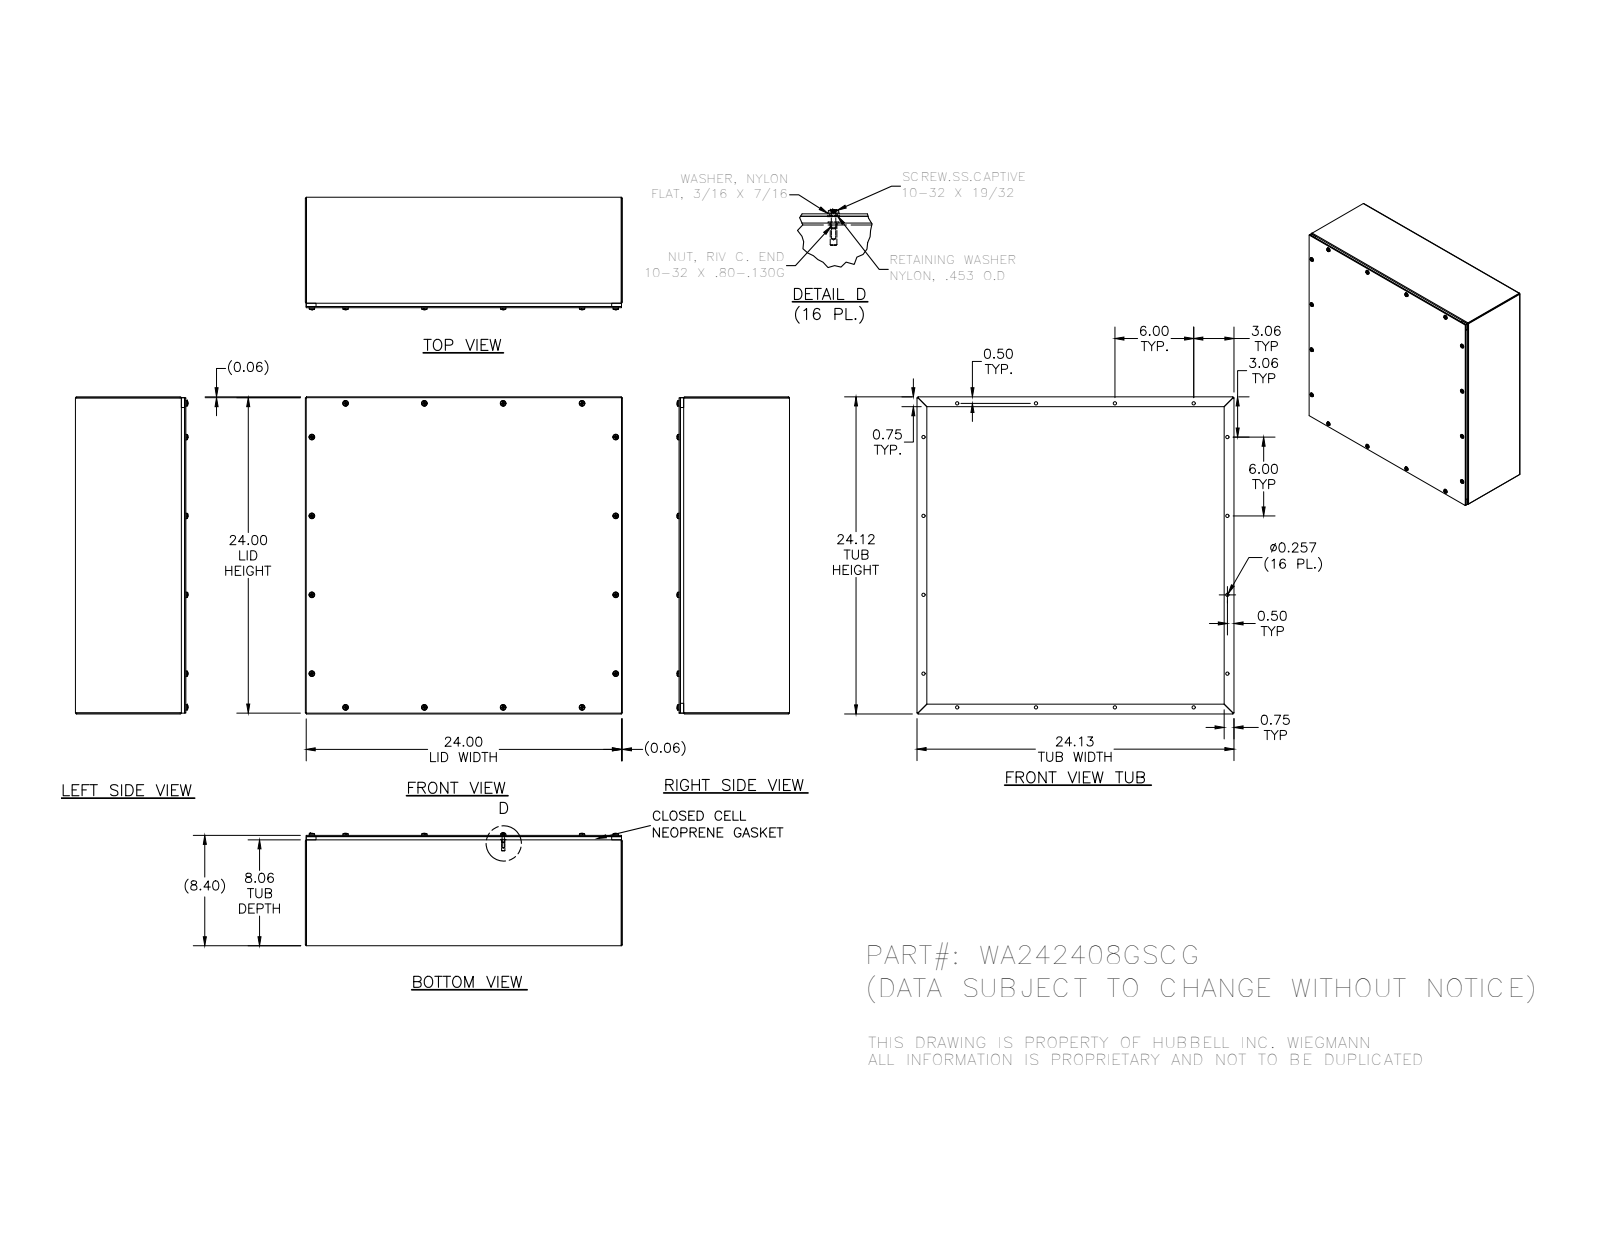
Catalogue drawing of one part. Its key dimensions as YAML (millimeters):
part_name: "WA242408GSCG; 34984; 39035; WA2424GSCGLP (+3 more)"
step_written_by: "SolidWorks 2014 (AUTOMOTIVE_DESIGN)"
units: millimeters
bodies: {solids: 70, faces: 1652, planar: 772, cylindrical: 432, other: 448}
overall_size: [612.8, 612.8, 217.4]
volume: 2899000
surface_area: 2723000
round_holes:
  - {diameter: 4, count: 16}
  - {diameter: 4.8, count: 16}
  - {diameter: 5, count: 16}
  - {diameter: 6.5, count: 16}
  - {diameter: 7.1, count: 16}
  - {diameter: 7.1, count: 16}
round_bosses_or_shafts:
  - {diameter: 11.5, count: 16}
  - {diameter: 11.1, count: 16}
  - {diameter: 10.3, count: 16}
  - {diameter: 6.3, count: 16}
  - {diameter: 4.2, count: 16}
partial_cylinders:
  - {radius: 2.3, count: 16}
  - {radius: 0.4, count: 8}
  - {radius: 2.3, count: 8}
face_to_face_distances: [1.9, 2.4, 211.6, 213.5, 209.2, 211.1, 609, 610.9, 610.9, 1.9]
hole_center_spacings: [152.4, 304.8, 606.8, 606.8, 587.4, 429.1, 429.1, 565.8]
